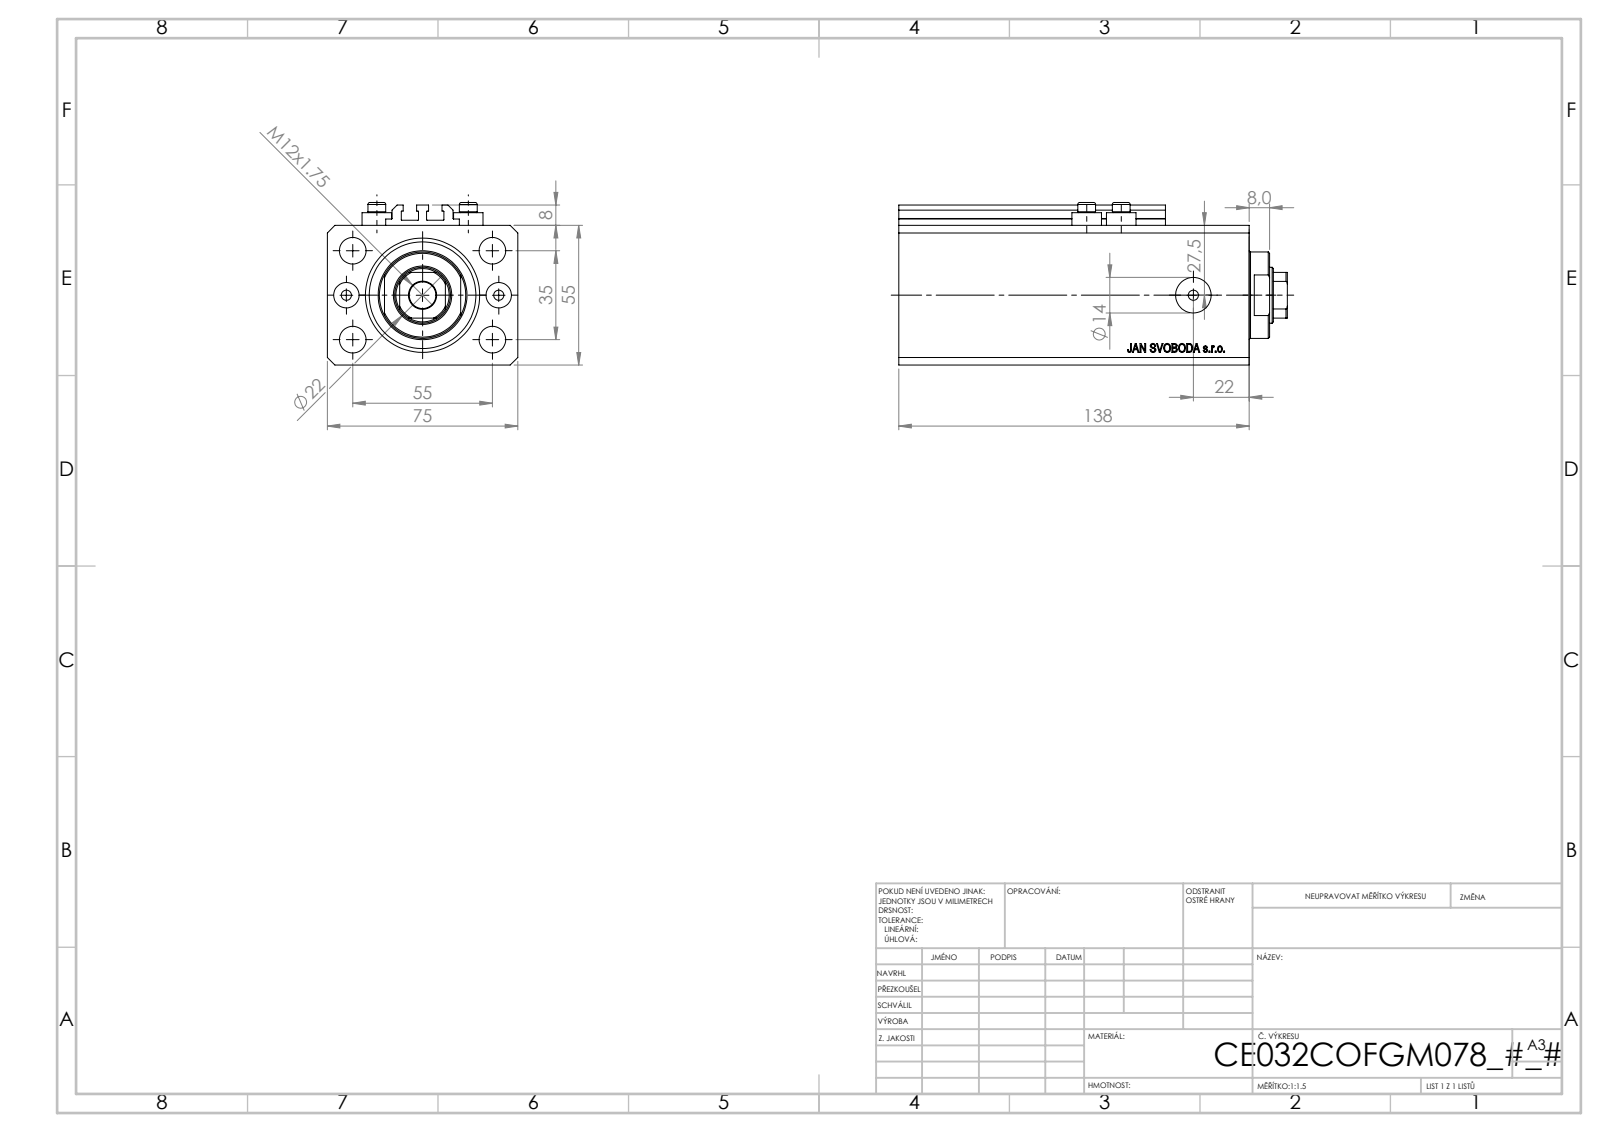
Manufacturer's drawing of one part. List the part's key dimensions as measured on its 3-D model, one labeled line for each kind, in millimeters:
Part name (STEP PRODUCT): V250CE_C_VCP; V250CE_C_Body; ALLEN BOLT V250CE; V250CE_VC_C
STEP written by: SolidWorks 2019 (CONFIG_CONTROL_DESIGN)
Units: millimetres
Bodies: 8 solids, 1034 faces (504 planar, 86 cylindrical, 444 other)
Overall size (bounding box): 153 × 75 × 64
Volume: 505 887 mm³ · Surface area: 109 467 mm²
Round holes (diameter × count): ⌀4 ×8, ⌀10.5 ×5, ⌀10 ×2, ⌀14 ×2, ⌀22 ×1, ⌀32 ×1, ⌀45 ×1
Round bosses / shafts (diameter × count): ⌀11.6 ×4, ⌀7 ×4, ⌀34 ×1
Partial cylindrical surfaces — rounded edges, fillets, slot ends (radius × count): R0.2 ×10, R10.5 ×1
Main face-to-face distances: 55, 75, 138, 15, 123, 9.9, 113.1, 128.1, 2.5, 2
Hole centre spacings: 17.68, 32.6, 60.1, 13.6, 30, 35, 36, 38.48
